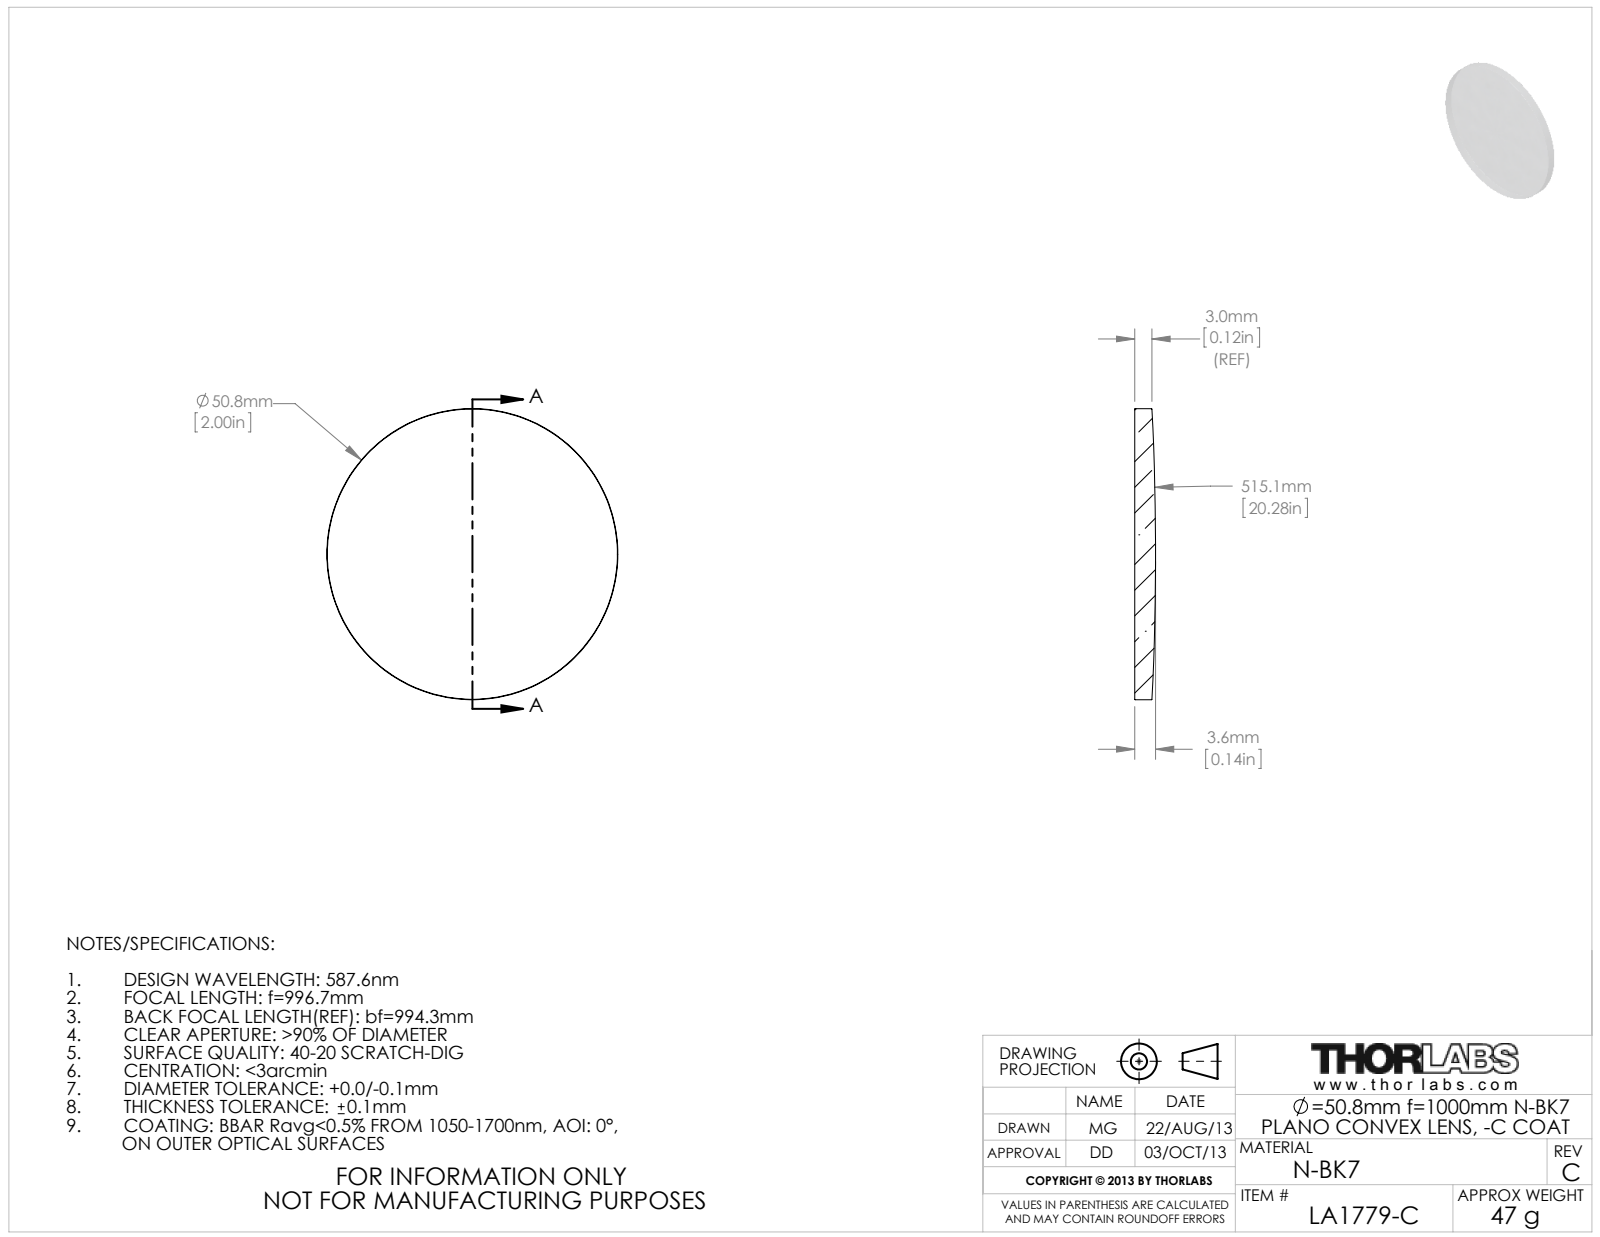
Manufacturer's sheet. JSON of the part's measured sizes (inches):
{"part_name": "4612-E0W", "step_written_by": "SolidWorks 2009 (AUTOMOTIVE_DESIGN)", "units": "inches", "bodies": {"solids": 0, "faces": 5, "planar": 1, "cylindrical": 2, "other": 2}, "overall_size": [2, 2, 0.143], "round_bosses_or_shafts": [[2, 1]]}
